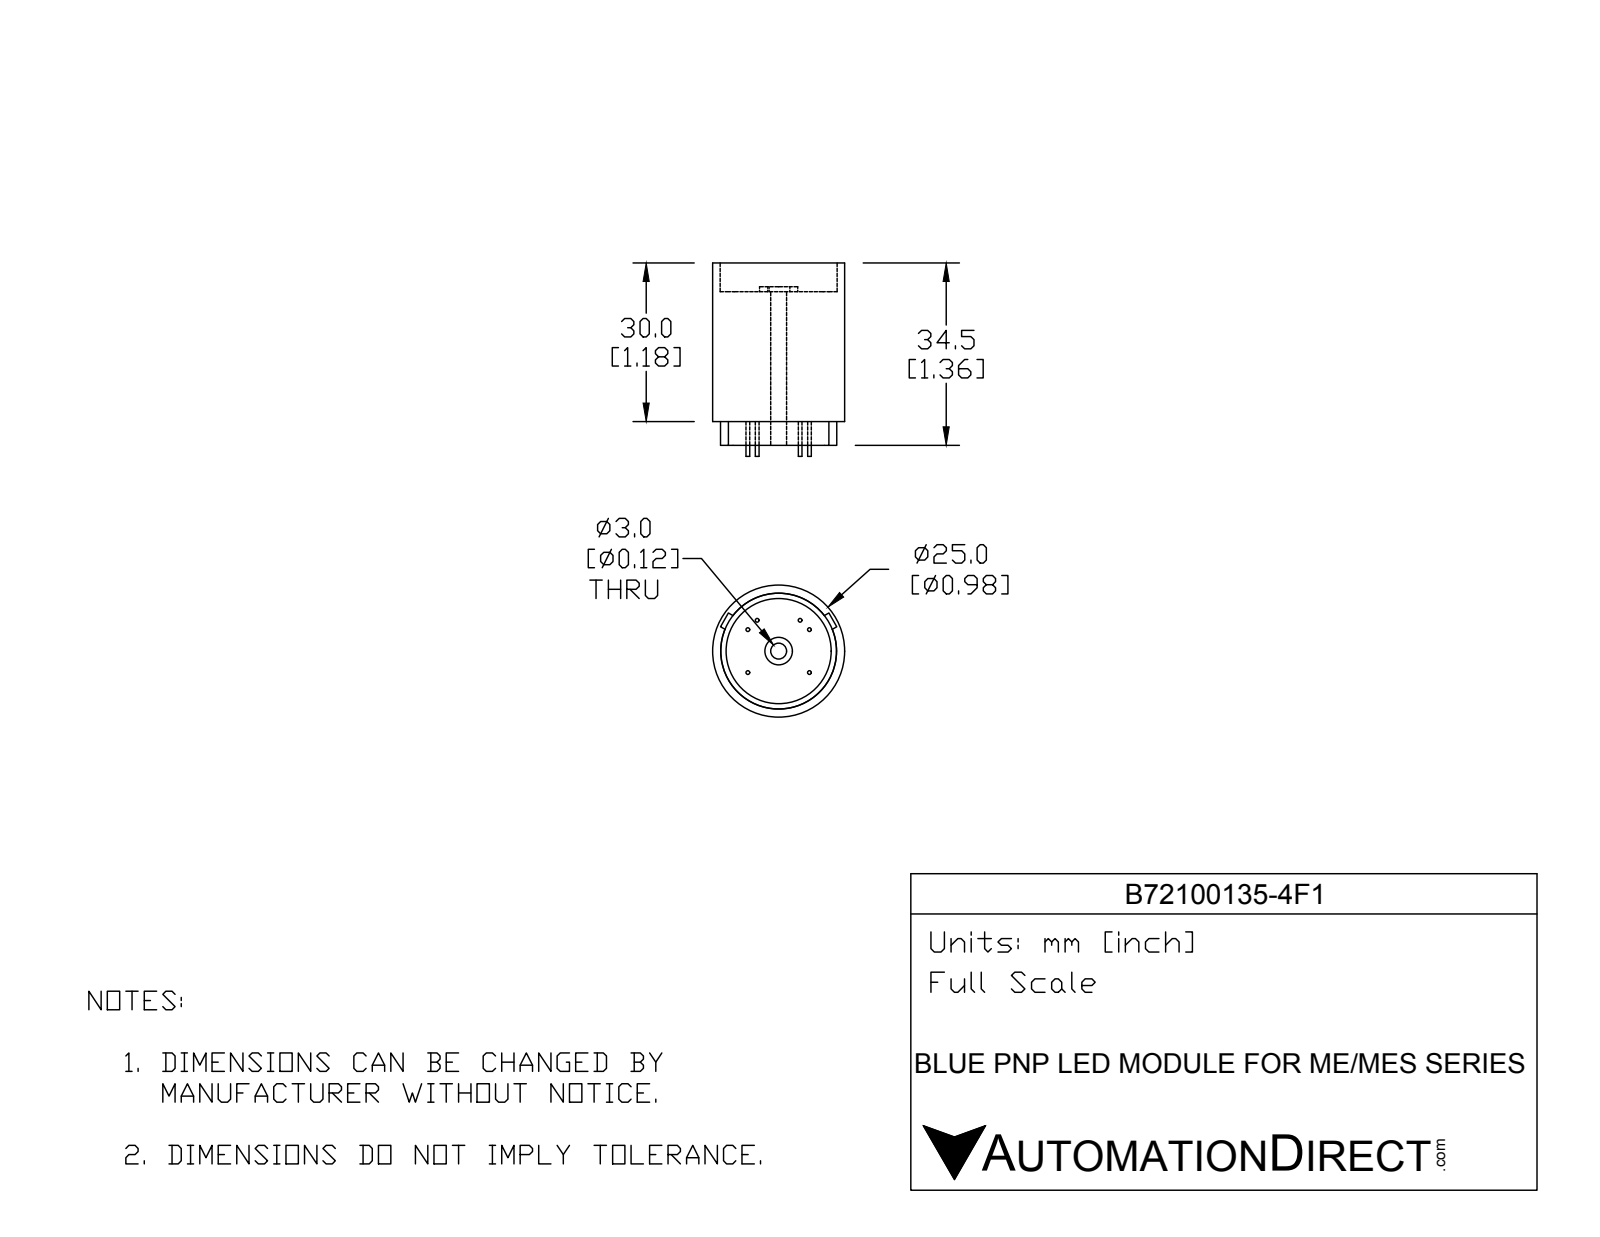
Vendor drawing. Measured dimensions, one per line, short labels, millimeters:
name: B72100135-4F1
written by: SolidWorks 2016 (AUTOMOTIVE_DESIGN)
unit: mm
bodies: 9 solids, 69 faces (36 planar, 33 cylindrical, 0 other)
size: 36.6 × 25 × 25
volume: 12 963 mm³; area: 4 884 mm²
holes: 1× ⌀3, 1× ⌀4.22, 1× ⌀19.9, 1× ⌀21.5
bosses: 6× ⌀0.7, 1× ⌀25, 1× ⌀21.9, 1× ⌀7.22, 1× ⌀5.2
face distances: 24.56, 30, 5.44, 4.5, 29.06, 34.5, 25.5, 0.94, 3.05, 3.1
